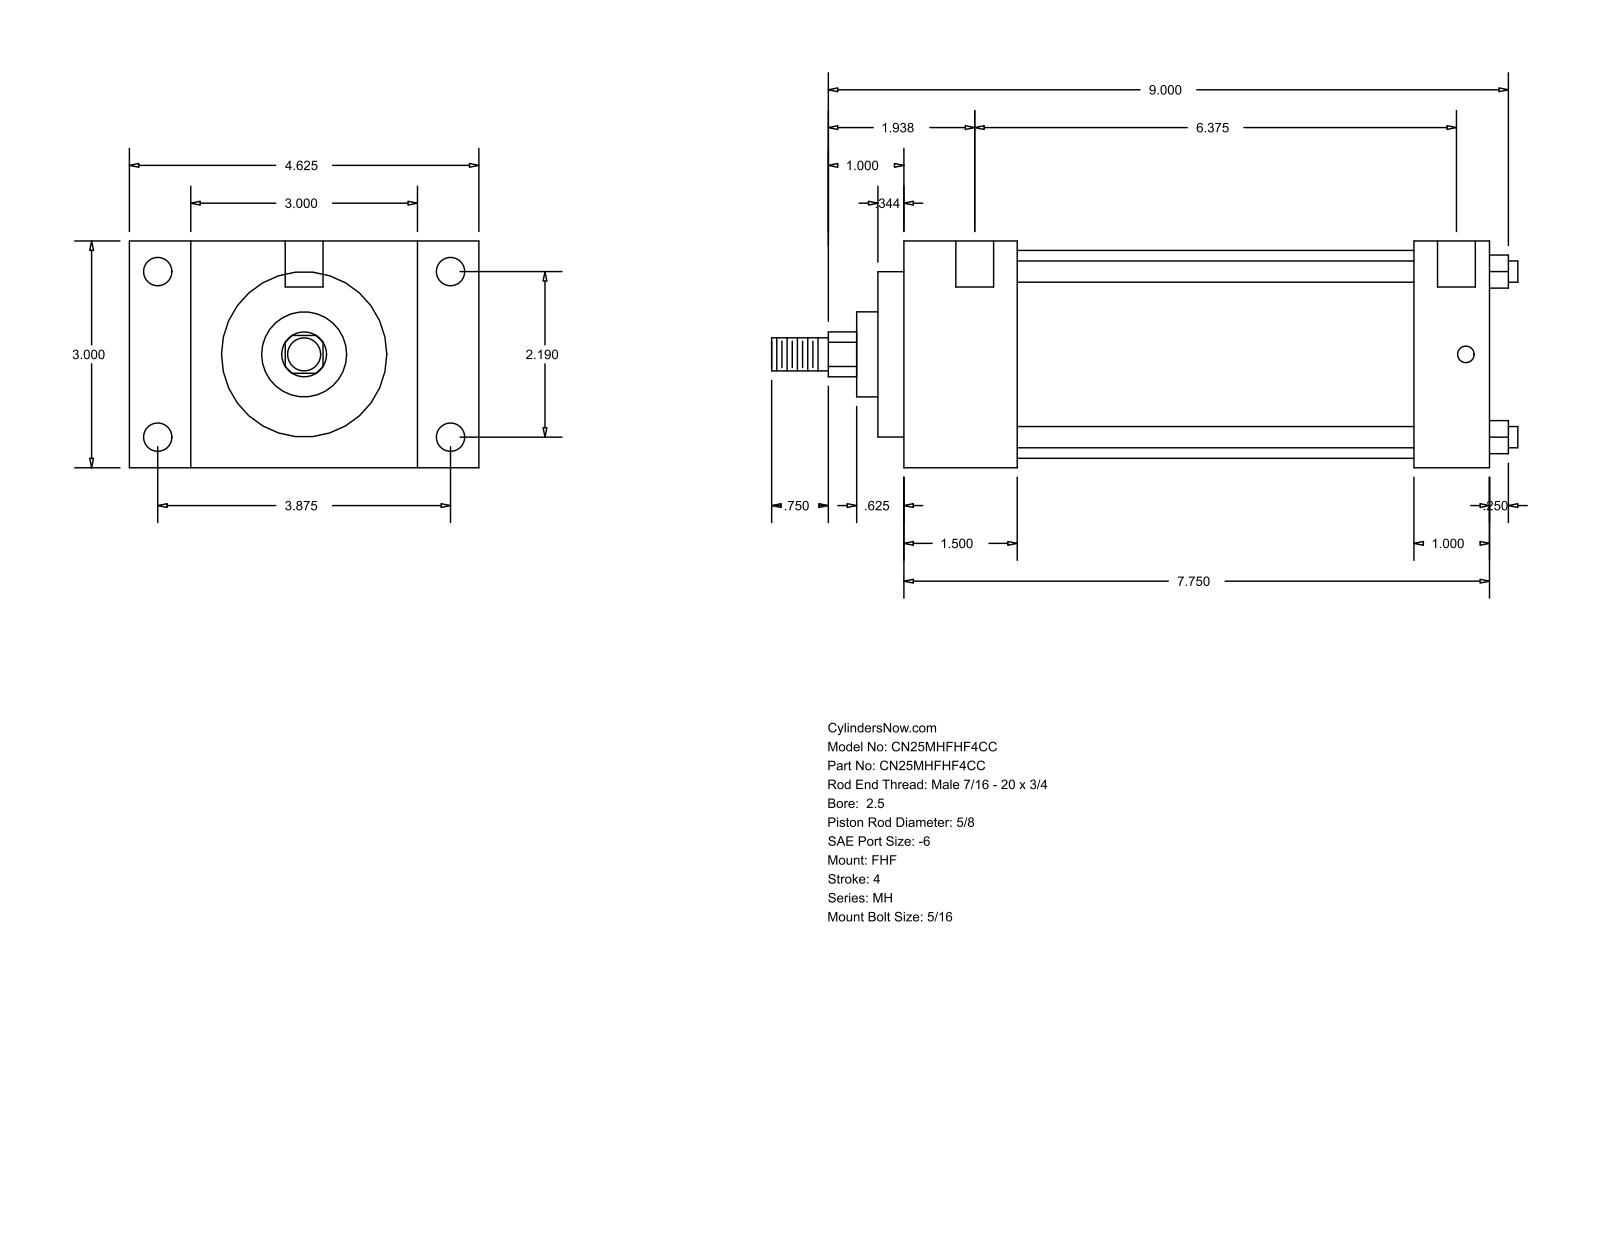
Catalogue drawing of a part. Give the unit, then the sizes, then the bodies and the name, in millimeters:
Units: millimetres
Overall size (bounding box): 250.82 × 117.47 × 76.2
Round holes (diameter × count): ⌀5.56 ×4, ⌀9.53 ×4, ⌀12.7 ×2
Round bosses / shafts (diameter × count): ⌀7.14 ×4, ⌀69.85 ×1, ⌀55.55 ×1, ⌀28.57 ×1, ⌀15.88 ×1, ⌀11.11 ×1
Partial cylindrical surfaces — rounded edges, fillets, slot ends (radius × count): R7.54 ×1
Main face-to-face distances: 76.2, 196.85, 38.1, 158.75, 20.64, 96.84, 117.48, 25.4, 171.45, 133.35
Hole centre spacings: 55.62, 98.42, 113.05, 169.86, 3.17, 4.76, 161.93, 165.1
Bodies: 0 solids, 90 faces (61 planar, 29 cylindrical, 0 other)
Part name (STEP PRODUCT): MH_FHF__0250_0.625
STEP written by: GSSL Pune (CONFIG_CONTROL_DESIGN)
